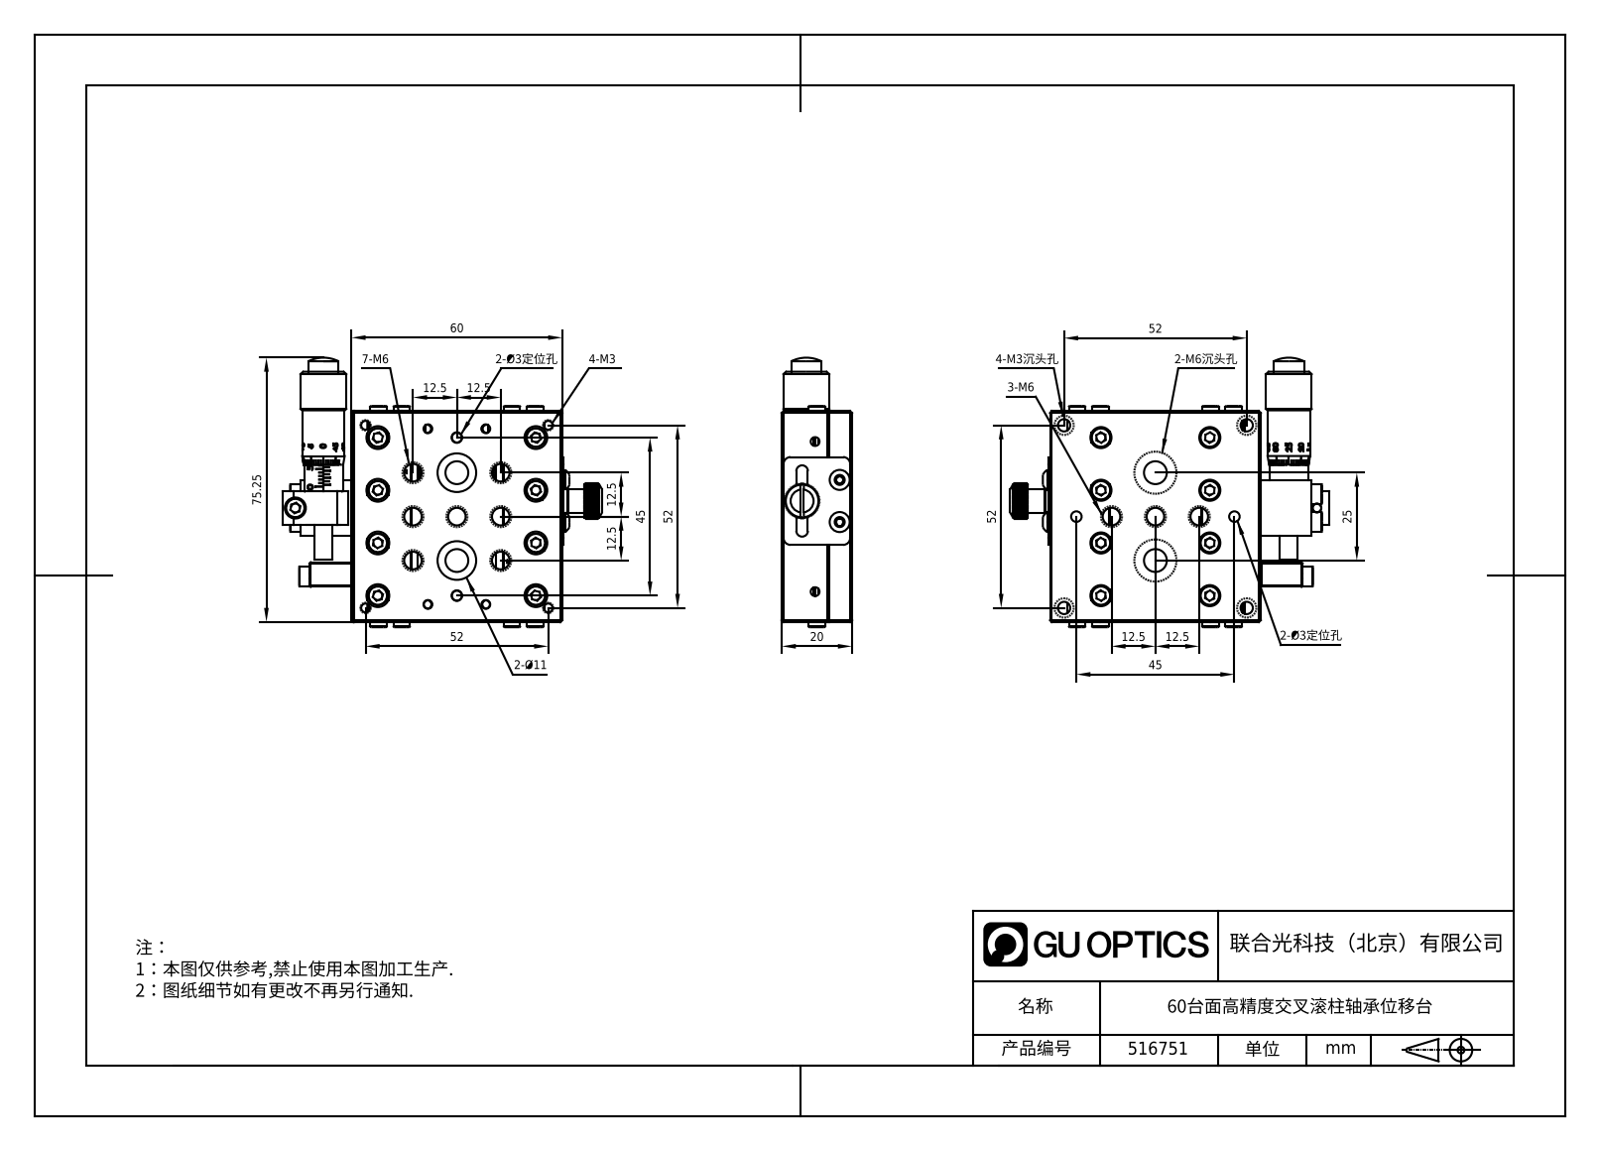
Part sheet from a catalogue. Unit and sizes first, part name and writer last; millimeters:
Units: millimetres
Overall size (bounding box): 90.9 × 76.75 × 20
Round holes (diameter × count): ⌀4.7 ×4, ⌀2 ×2
Round bosses / shafts (diameter × count): ⌀2.5 ×14, ⌀5.5 ×11, ⌀6.5 ×10, ⌀6 ×9, ⌀5 ×8, ⌀3.5 ×8, ⌀3.3 ×4, ⌀3 ×4
Partial cylindrical surfaces — rounded edges, fillets, slot ends (radius × count): R2 ×4, R1.65 ×2, R5 ×1, R5.49 ×1, R6.04 ×1
Main face-to-face distances: 7, 13, 6.5, 20, 0.5, 6.55, 6.45, 13.45, 6, 13.5
Hole centre spacings: 6.6, 38, 31.4, 43, 44.6
Bodies: 0 solids, 1228 faces (791 planar, 183 cylindrical, 254 other)
Part name (STEP PRODUCT): 516751 (1)
STEP written by: SolidWorks 2020 (CONFIG_CONTROL_DESIGN)
